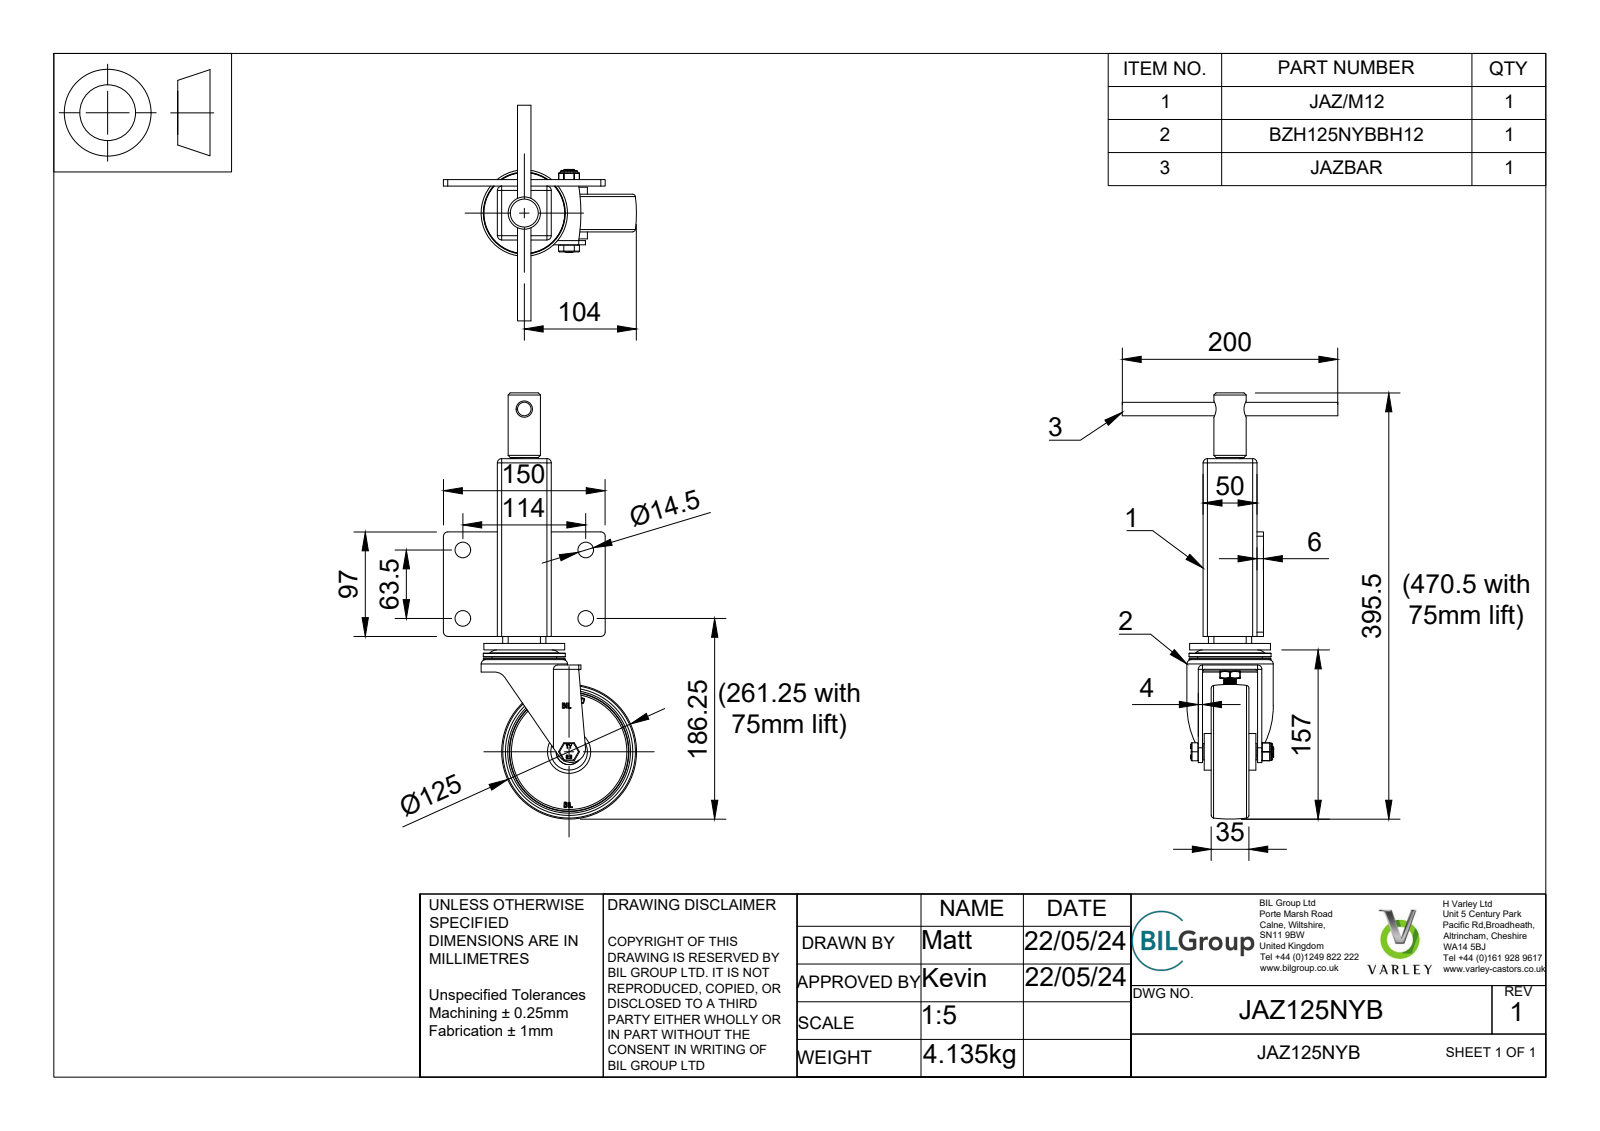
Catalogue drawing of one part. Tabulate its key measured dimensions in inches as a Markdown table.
| quantity | value |
| --- | --- |
| part name | JAZ125NYB v5; JAZM12 v2; ZINC PLATED BOX JACKING UNIT; BACK PLATE (+8 more) |
| STEP written by | Autodesk Translation Framework v13.14.0.145 (AUTOMOTIVE_DESIGN) |
| units | inches |
| bodies | 26 solids, 817 faces (321 planar, 309 cylindrical, 187 other) |
| overall size | 15.571 × 7.874 × 7.047 |
| volume | 41.03 in³ |
| surface area | 475.6 in² |
| round holes (diameter × count) | 0.571 × 4, 0.472 × 2, 0.394 × 1, 0.402 × 1, 0.413 × 1, 0.476 × 1, 0.591 × 1, 0.594 × 1, 1.26 × 1, 1.496 × 1, 2.283 × 1, 2.835 × 1 |
| round bosses / shafts (diameter × count) | 0.157 × 8, 3.15 × 1, 2.992 × 1, 2.953 × 1, 2.362 × 1, 1.988 × 1, 1.535 × 1, 1.339 × 1 |
| partial cylindrical surfaces (radius × count) | 0.02 × 24, 0.157 × 14, 0.098 × 8, 0.03 × 6, 0.079 × 4, 0.197 × 4, 0.369 × 1, 0.472 × 1 |
| main face-to-face distances | 0.098, 0.197, 1.87, 1.772, 1.673, 0.236, 1.575, 0.807, 0.295, 0.709 |
| hole center spacings | 2.5, 4.488, 5.137, 5.614, 7.968, 4.91, 6.227, 7.397 |
